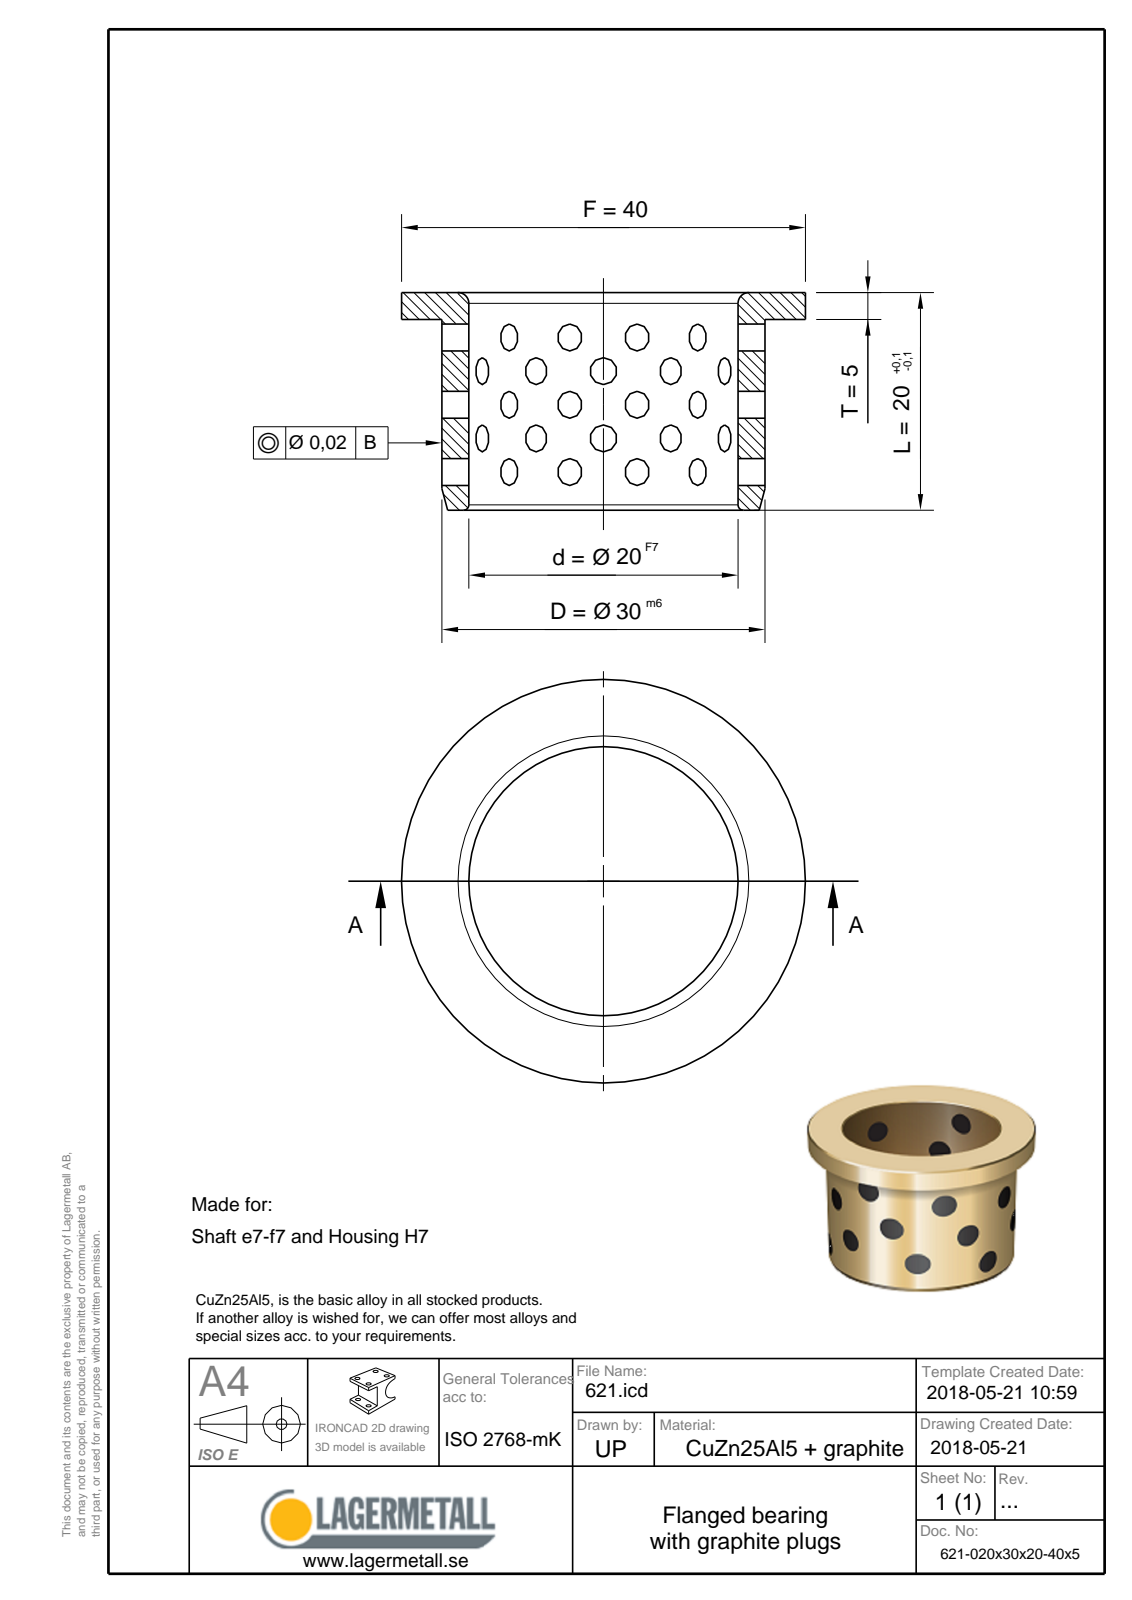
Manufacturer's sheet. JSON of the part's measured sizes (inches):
{"part_name": "621-020x30x20-40x5", "step_written_by": "Spatial InterOp 3D (CONFIG_CONTROL_DESIGN)", "units": "inches", "bodies": {"solids": 1, "faces": 9, "planar": 3, "cylindrical": 3, "other": 3}, "overall_size": [1.575, 1.575, 0.787], "volume_in3": 0.639, "surface_area_in2": 7.815, "round_holes": [[0.787, 1]], "round_bosses_or_shafts": [[1.575, 1], [1.181, 1]], "face_to_face_distances": [0.197, 0.591, 0.787]}
